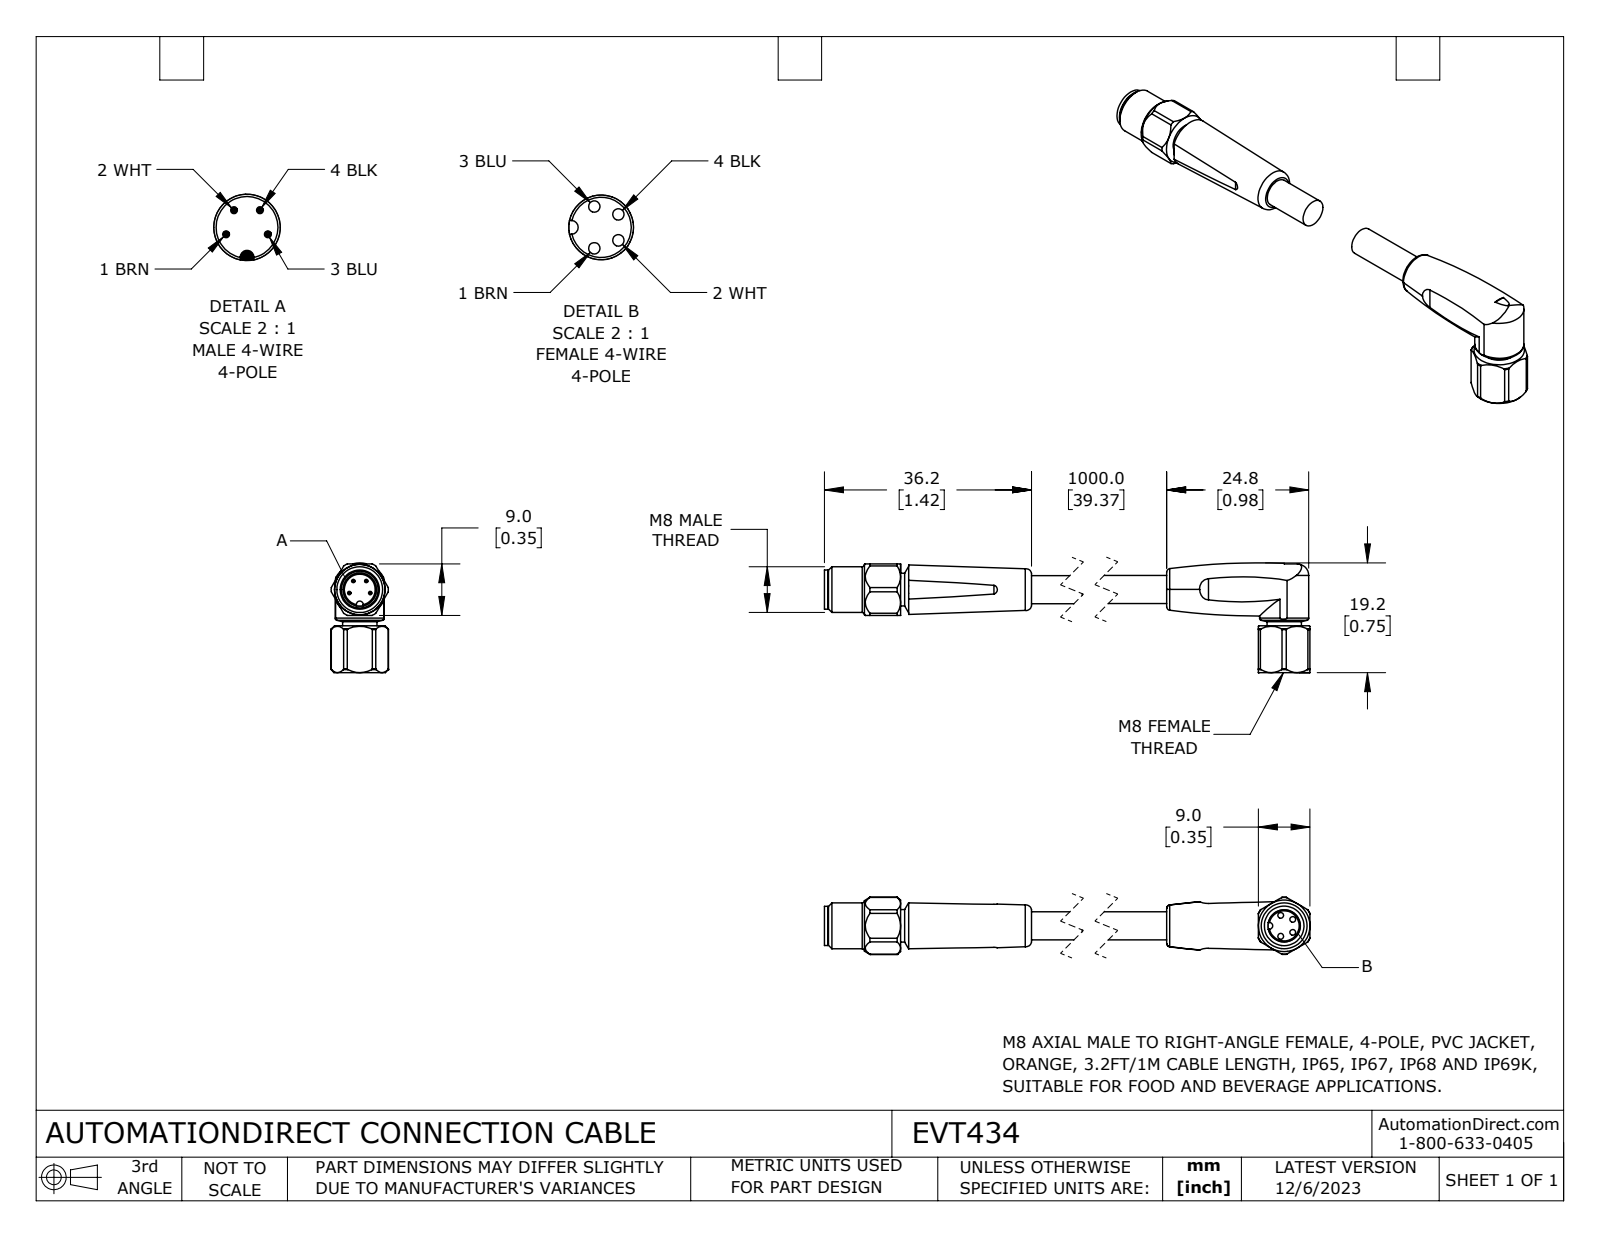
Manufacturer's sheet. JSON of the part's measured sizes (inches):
{"part_name": "EVT434_MALE; EVT434_FEMALE; EVT434", "step_written_by": "SolidWorks 2023 (CONFIG_CONTROL_DESIGN)", "units": "inches", "bodies": {"solids": 2, "faces": 172, "planar": 52, "cylindrical": 59, "other": 61}, "overall_size": [3.76, 0.755, 0.394], "volume_in3": 0.254, "surface_area_in2": 4.6, "round_holes": [[0.039, 4], [0.228, 1], [0.272, 1]], "round_bosses_or_shafts": [[0.023, 4], [0.193, 2], [0.339, 1], [0.315, 1], [0.27, 1], [0.248, 1], [0.236, 1], [0.224, 1]], "partial_cylinders_radius": [[0.024, 2], [0.126, 2], [0.133, 2], [0.196, 1], [0.197, 1]], "face_to_face_distances": [0.354, 0.354, 3.236, 2.882, 0.323, 0.748, 0.425, 0.394, 0.071, 0.327], "hole_center_spacings": [0.074, 0.076, 0.087, 0.143, 0.089, 0.143]}
